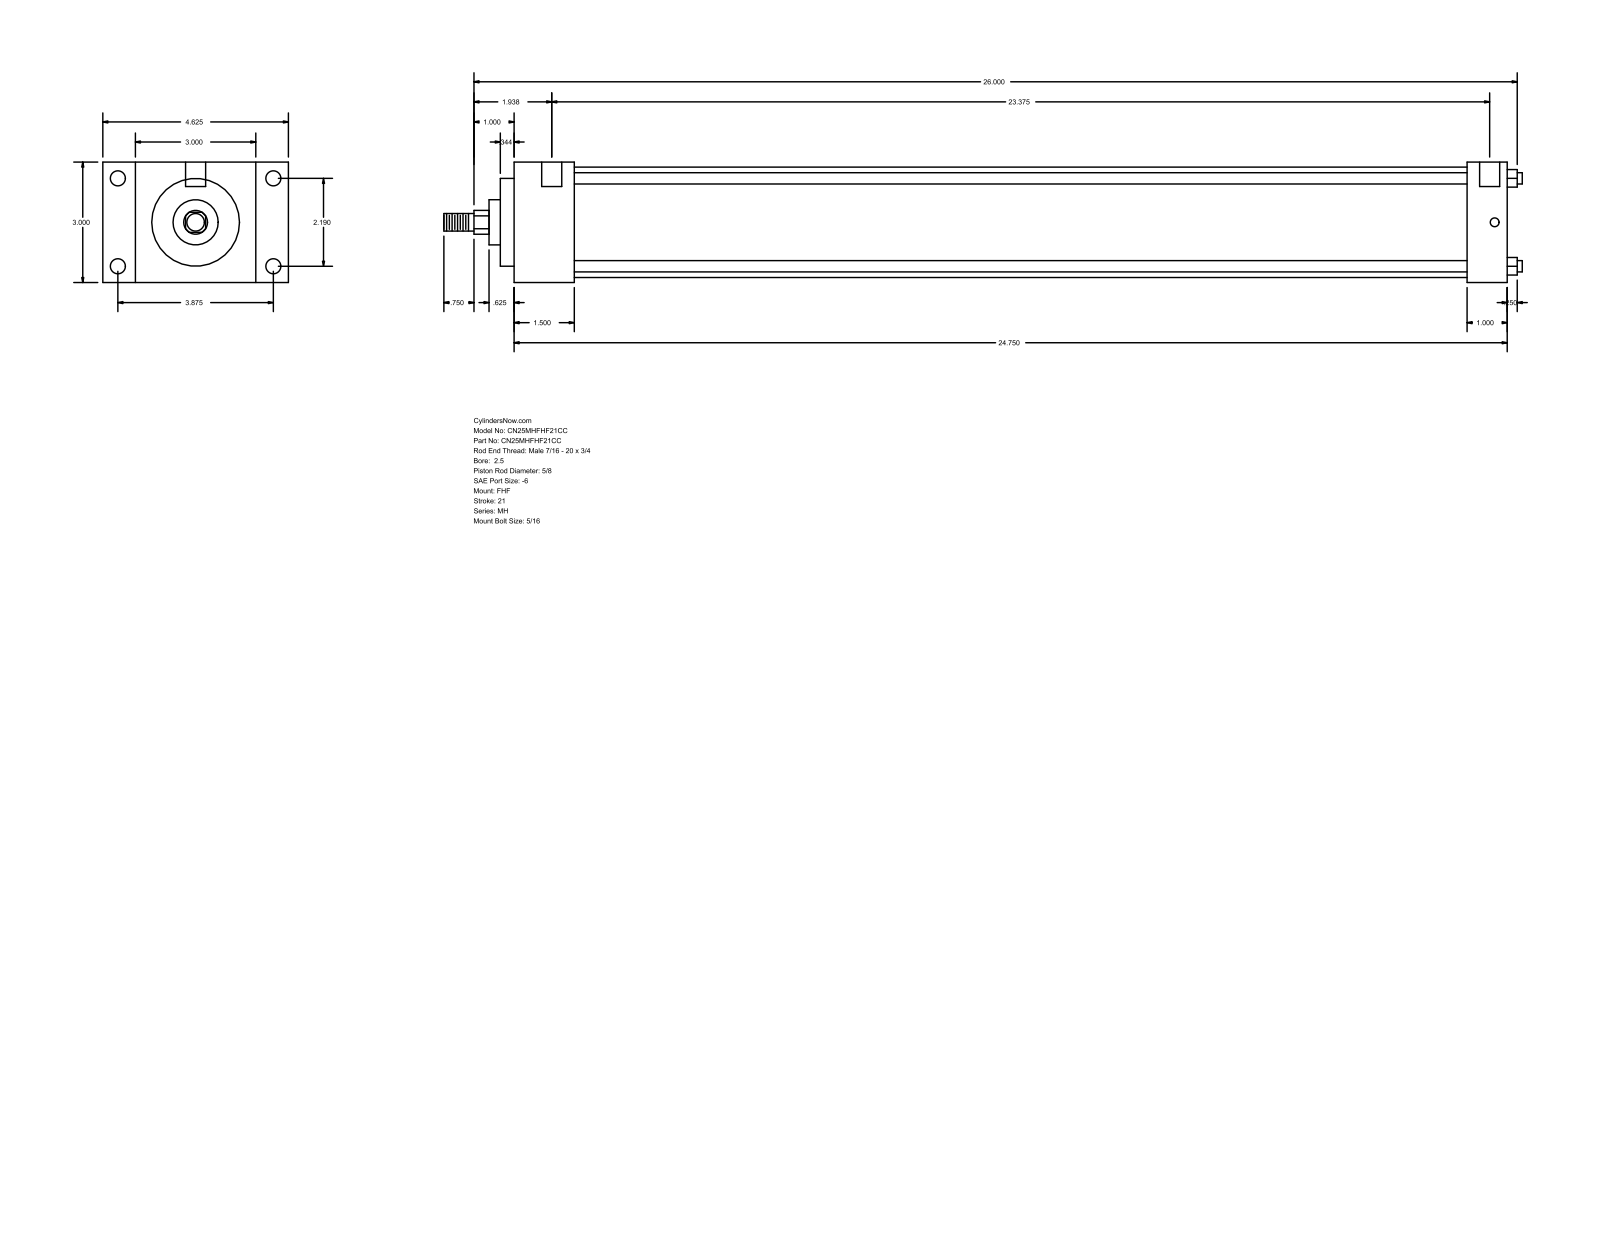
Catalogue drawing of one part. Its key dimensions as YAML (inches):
part_name: "MH_FHF__0250_0.625"
step_written_by: "GSSL Pune (CONFIG_CONTROL_DESIGN)"
units: inches
bodies: {solids: 0, faces: 90, planar: 61, cylindrical: 29, other: 0}
overall_size: [26.875, 4.625, 3]
round_holes:
  - {diameter: 0.219, count: 4}
  - {diameter: 0.375, count: 4}
  - {diameter: 0.5, count: 2}
round_bosses_or_shafts:
  - {diameter: 0.281, count: 4}
  - {diameter: 2.75, count: 1}
  - {diameter: 2.187, count: 1}
  - {diameter: 1.125, count: 1}
  - {diameter: 0.625, count: 1}
  - {diameter: 0.437, count: 1}
partial_cylinders:
  - {radius: 0.297, count: 1}
face_to_face_distances: [3, 24.75, 1.5, 23.25, 0.813, 3.813, 4.625, 1, 23.75, 22.25]
hole_center_spacings: [2.19, 3.875, 4.451, 23.687, 0.125, 0.187, 23.375, 23.5]
